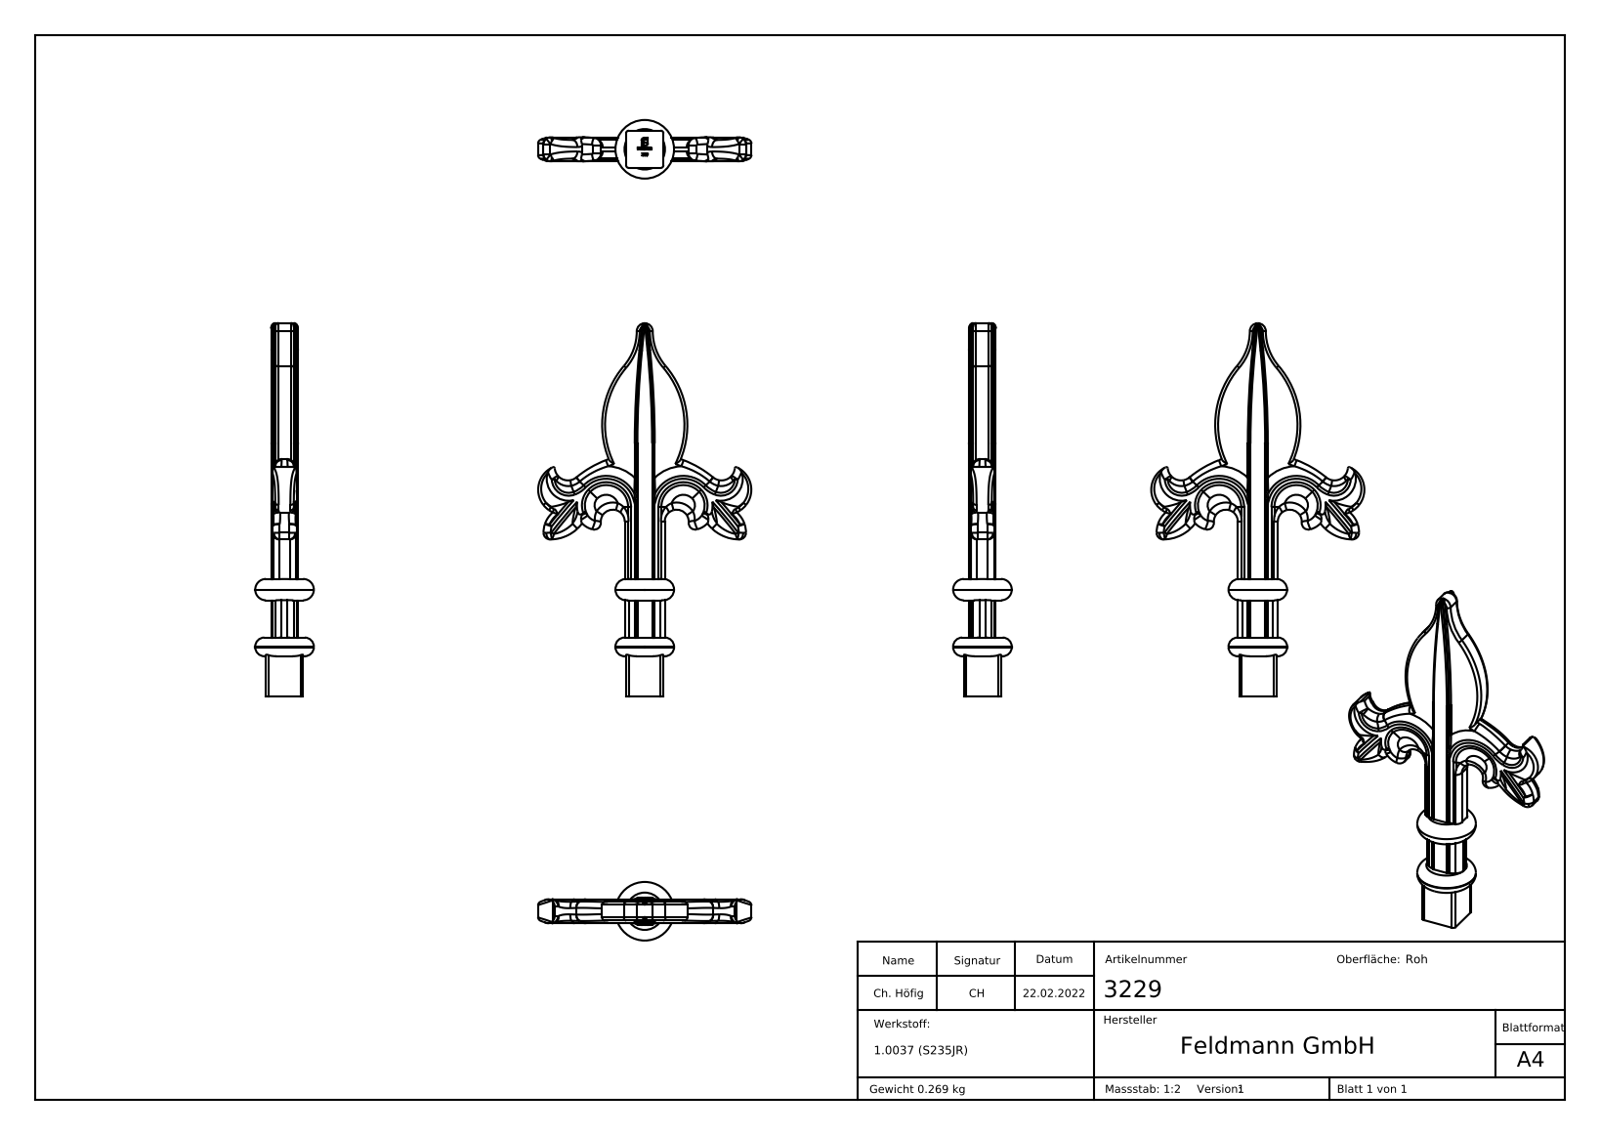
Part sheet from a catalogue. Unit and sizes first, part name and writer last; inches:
Units: inches
Overall size (bounding box): 5.512 × 3.15 × 0.866
Round bosses / shafts (diameter × count): ⌀0.866 ×1
Partial cylindrical surfaces — rounded edges, fillets, slot ends (radius × count): R0.02 ×24, R0.098 ×12, R0.106 ×8, R0.039 ×4, R0.354 ×4, R0.177 ×2, R0.197 ×2, R0.315 ×2
Main face-to-face distances: 0.059, 0.335, 0.276, 0.02, 0.315, 0.374, 0.039, 0.394, 0.551, 0.079
Volume: 2.101 in³ · Surface area: 18.38 in²
Bodies: 1 solid, 626 faces (164 planar, 83 cylindrical, 379 other)
Part name (STEP PRODUCT): 3229
STEP written by: SolidWorks 2018 (CONFIG_CONTROL_DESIGN)
